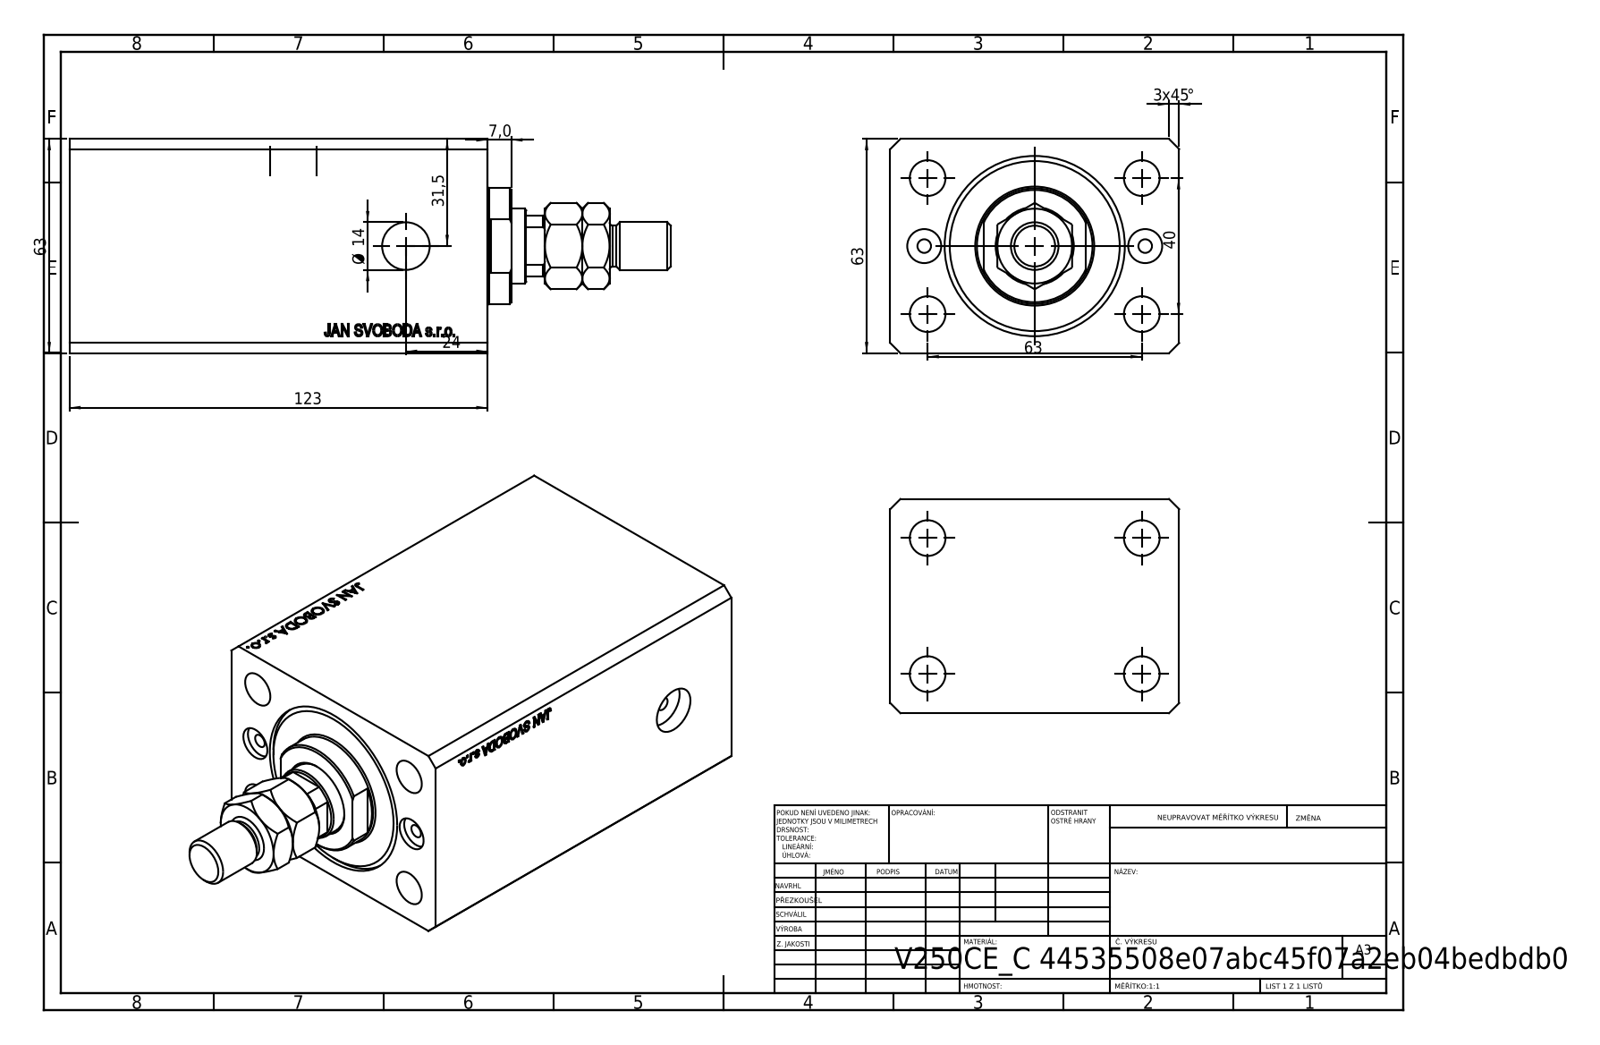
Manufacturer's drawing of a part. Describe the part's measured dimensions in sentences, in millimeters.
The part is named "V250CE_VC_C; V250CE_C_VCP; V250CE_C_Body; MTA". Its 3-D file was written by "SolidWorks 2019 (CONFIG_CONTROL_DESIGN)". It is 4 solids with 911 faces: 443 planar, 46 cylindrical and 422 other. Overall it measures 176.9 by 85 by 63 millimeters. Its volume is 584 085 cubic millimeters and its surface area 107 301 square millimeters. Round holes: 4 of diameter 10.5, 3 of diameter 4, 2 of diameter 10, 2 of diameter 14, 1 of diameter 12.5, 1 of diameter 22, 1 of diameter 40, 1 of diameter 53. Round bosses or shafts: 1 of diameter 34, 1 of diameter 14, 1 of diameter 12. Partial cylindrical surfaces (rounded edges, fillets, slot ends): 1 of radius 10.5. The main face-to-face distances are 63, 85, 123, 95.9, 27.1, 11.4, 84.5, 111.6, 100.4, 50. The hole center spacings are 20.02, 37.31, 67.05, 32.5, 40, 63, 74.63, 65.
